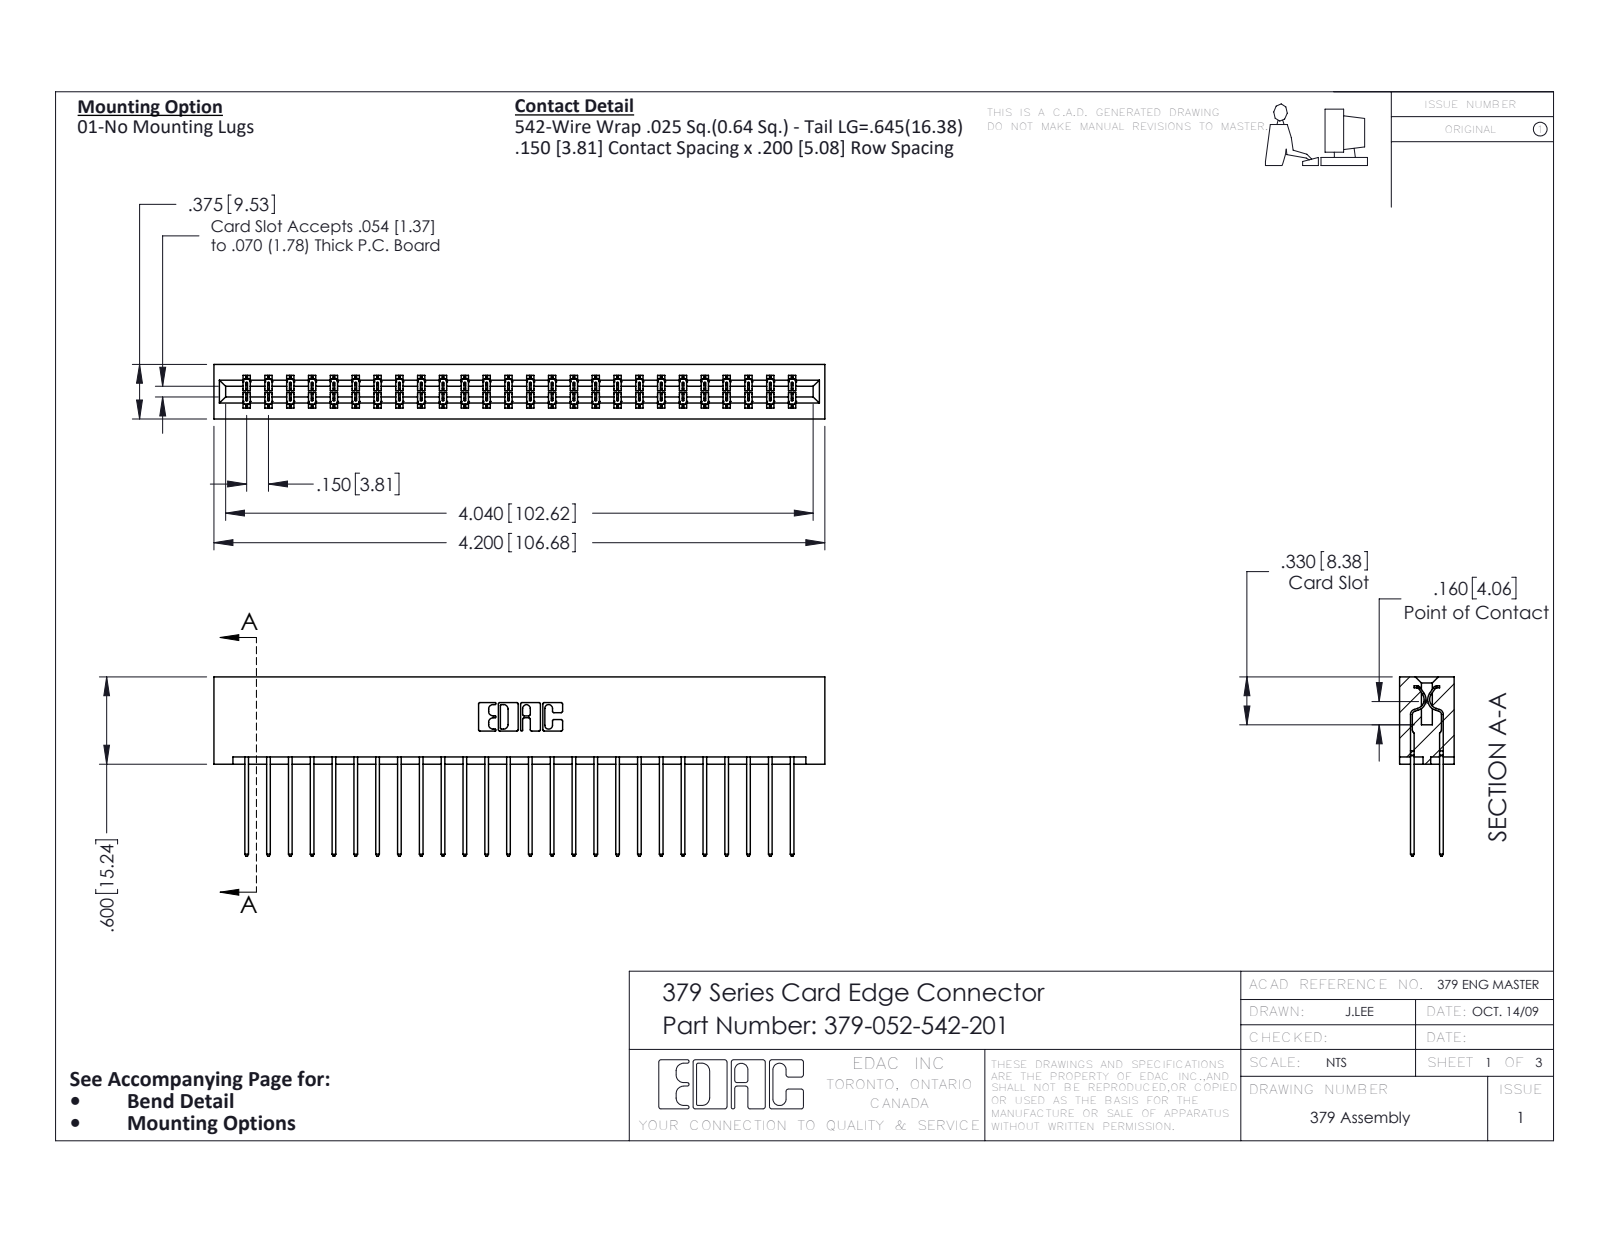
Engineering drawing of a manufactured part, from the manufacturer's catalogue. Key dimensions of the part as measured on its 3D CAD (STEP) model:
Part name (STEP PRODUCT): 379 Part_Lugless; 379-052-542-201; 345-292-001_345-293-142
STEP written by: SolidWorks 2016 (CONFIG_CONTROL_DESIGN)
Units: inches
Bodies: 53 solids, 2810 faces (1938 planar, 872 cylindrical, 0 other)
Overall size (bounding box): 4.2 × 1.232 × 0.375
Volume: 0.741 in³ · Surface area: 22.86 in²
Partial cylindrical surfaces — rounded edges, fillets, slot ends (radius × count): R0.006 ×78, R0.01 ×52, R0.01 ×22, R0.007 ×6, R0.031 ×6, R0.026 ×3, R0.014 ×2, R0.022 ×2
Main face-to-face distances: 0.3, 0.075, 0.1, 0.2, 0.375, 0.275, 0.025, 0.076, 0.15, 0.225
